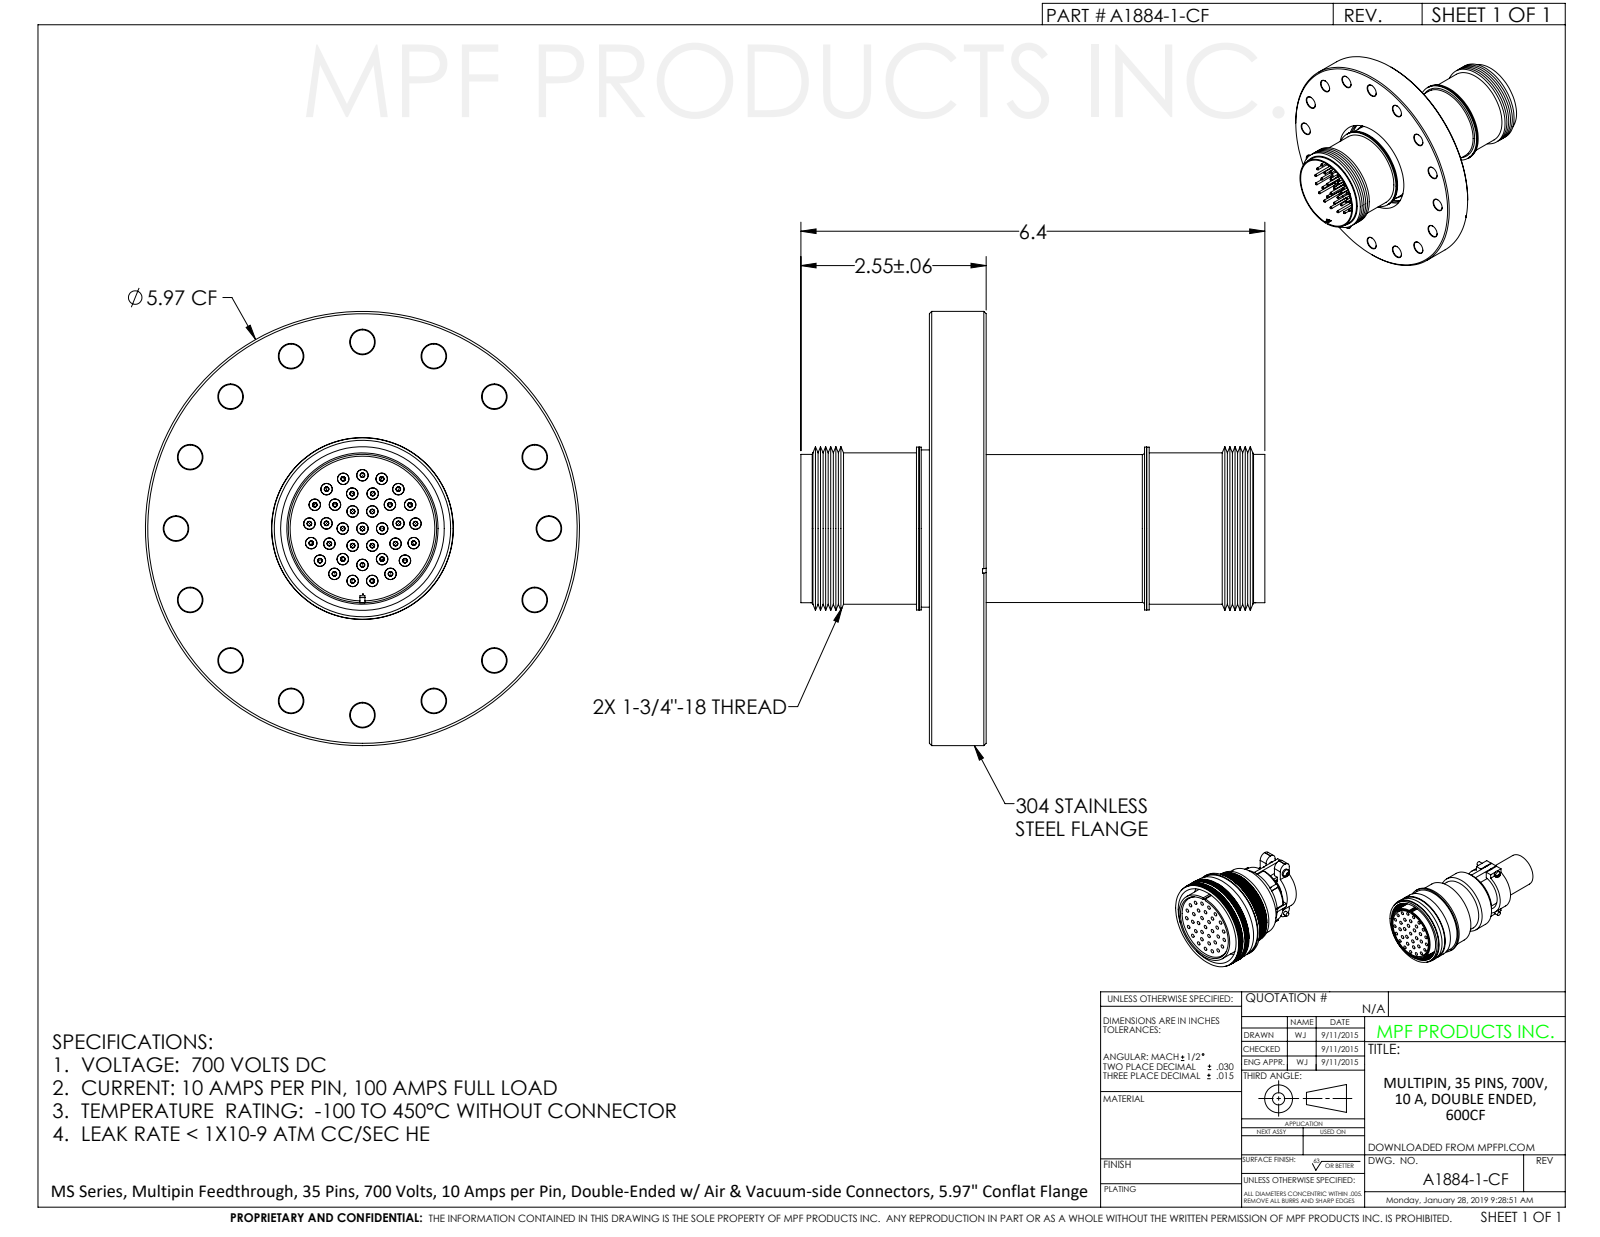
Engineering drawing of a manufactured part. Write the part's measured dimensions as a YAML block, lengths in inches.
part_name: "A1884-1-CF"
step_written_by: "SolidWorks 2012 (CONFIG_CONTROL_DESIGN)"
units: inches
bodies: {solids: 1, faces: 1378, planar: 294, cylindrical: 746, other: 338}
overall_size: [6.38, 5.97, 5.97]
volume: 20.89
surface_area: 236.2
round_holes:
  - {diameter: 0.06, count: 18}
  - {diameter: 0.328, count: 16}
  - {diameter: 1.893, count: 1}
  - {diameter: 1.98, count: 1}
  - {diameter: 2.025, count: 1}
  - {diameter: 2.03, count: 1}
  - {diameter: 2.425, count: 1}
  - {diameter: 2.485, count: 1}
  - {diameter: 4.54, count: 1}
  - {diameter: 4.75, count: 1}
round_bosses_or_shafts:
  - {diameter: 0.187, count: 35}
  - {diameter: 0.171, count: 35}
  - {diameter: 0.056, count: 35}
  - {diameter: 5.97, count: 1}
  - {diameter: 2.24, count: 1}
  - {diameter: 2.205, count: 1}
  - {diameter: 2.16, count: 1}
  - {diameter: 2.08, count: 1}
partial_cylinders:
  - {radius: 0.03, count: 17}
face_to_face_distances: [0.729, 0.78, 0.051, 0.611, 1.34, 1.391, 4.06, 3.449, 2.72, 2.669]
hole_center_spacings: [1, 4.264, 4.738, 5.03, 1.963, 2.564, 3.626, 2.849]
